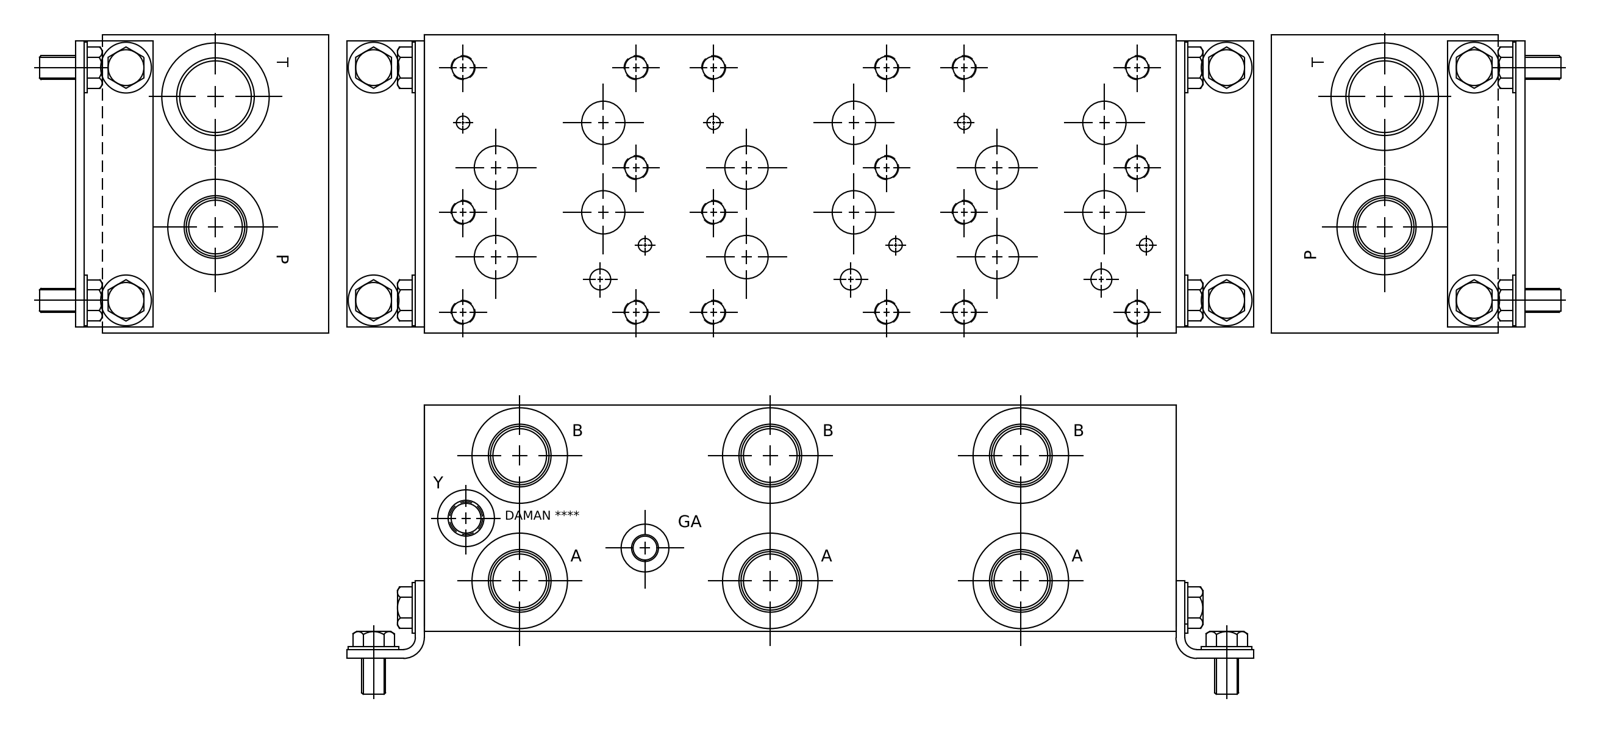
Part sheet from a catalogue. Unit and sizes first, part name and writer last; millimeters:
Units: millimetres
Overall size (bounding box): 400.05 × 158.75 × 120.65
Round holes (diameter × count): ⌀10.72 ×21, ⌀12.7 ×20, ⌀23.01 ×11, ⌀31.27 ×7, ⌀33.76 ×7, ⌀49.12 ×7, ⌀7.14 ×6, ⌀28.57 ×6, ⌀33.35 ×6, ⌀35.51 ×6, ⌀11.13 ×2, ⌀33.34 ×2
Main face-to-face distances: 120.65, 158.75, 400.05, 0.79, 157.96, 399.26, 398.47, 19.84, 19.05, 90.42
Hole centre spacings: 133.35, 266.7, 61.92, 74.63, 118.29, 152.7, 191.98, 29.53
Volume: 7 172 000 mm³ · Surface area: 341 647 mm²
Bodies: 1 solid, 823 faces (402 planar, 131 cylindrical, 290 other)
Part name (STEP PRODUCT): Part_DD08P035S_3D
STEP written by: Autodesk Inventor 2019 (AUTOMOTIVE_DESIGN)
